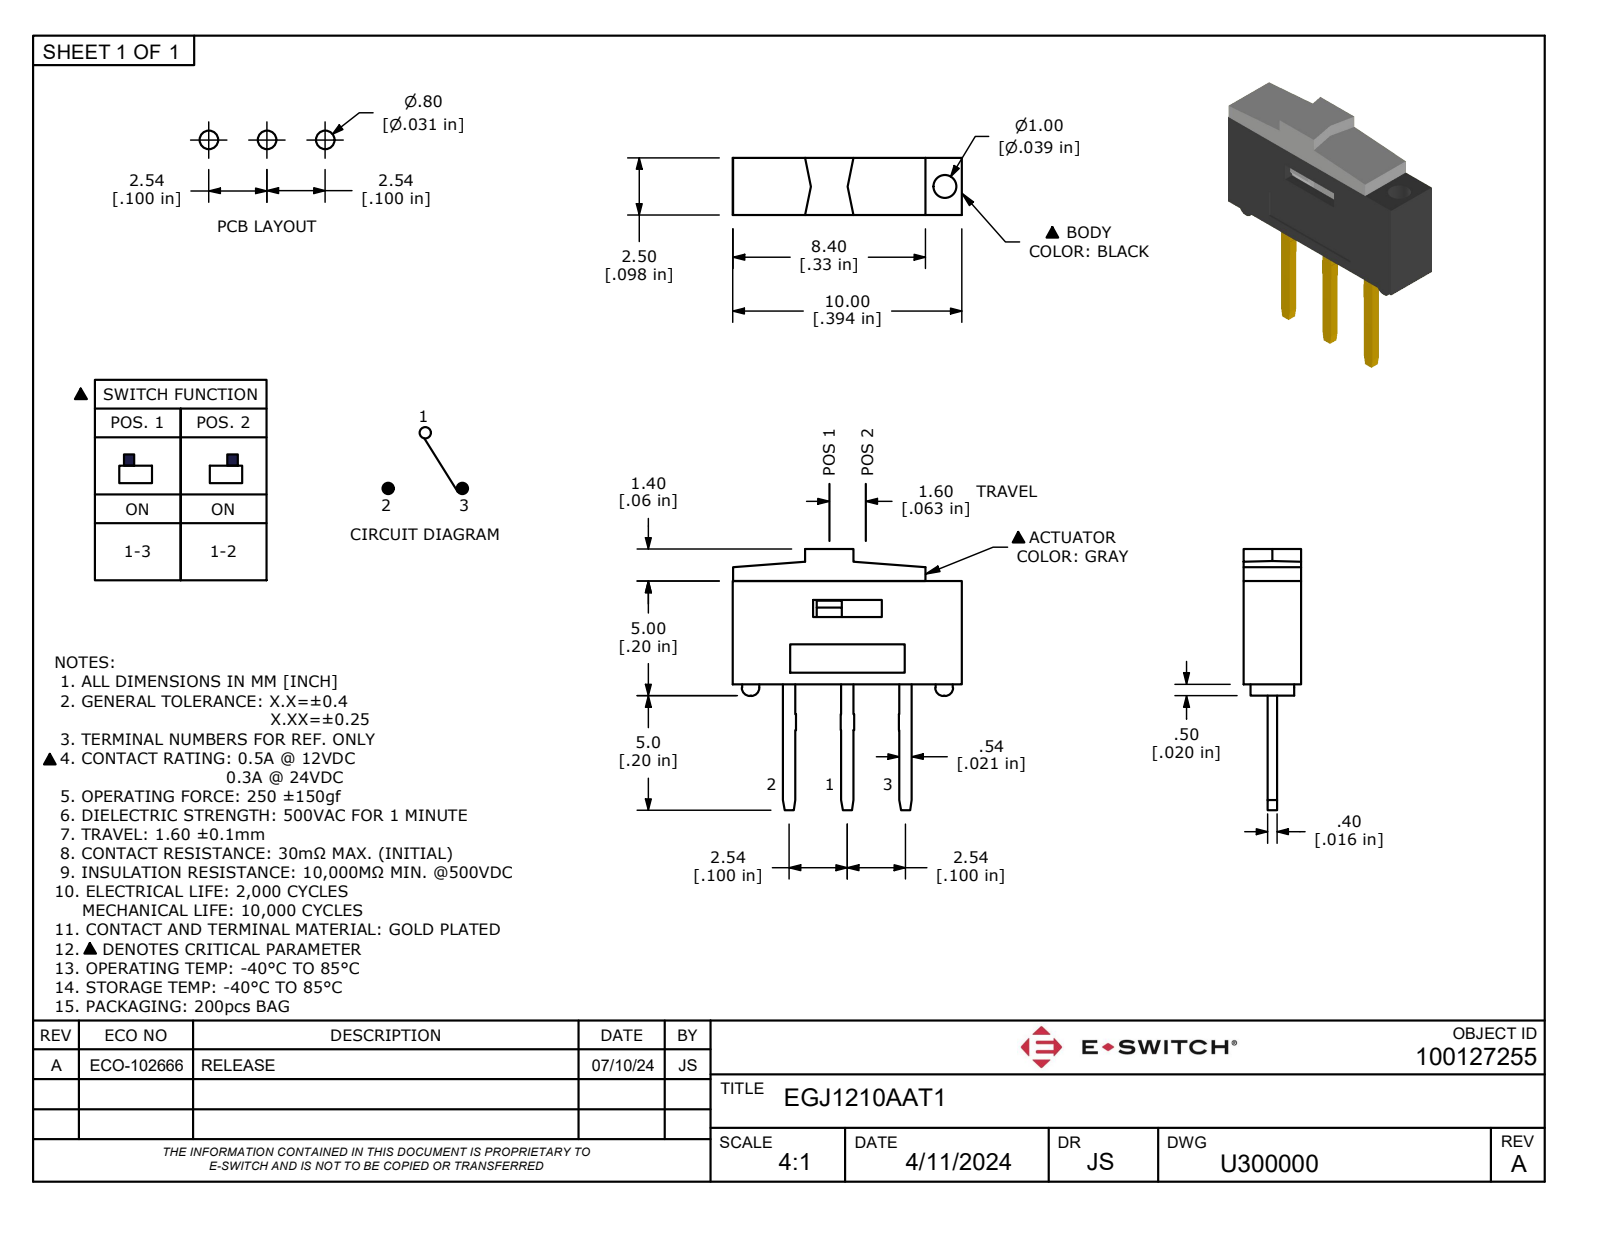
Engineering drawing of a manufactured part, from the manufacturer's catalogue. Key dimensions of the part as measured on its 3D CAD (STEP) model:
Part name (STEP PRODUCT): EGJ1210AAT1
STEP written by: Autodesk Inventor 2022 (AUTOMOTIVE_DESIGN)
Units: inches
Bodies: 1 solid, 105 faces (100 planar, 5 cylindrical, 0 other)
Overall size (bounding box): 0.449 × 0.394 × 0.098
Volume: 0.006 in³ · Surface area: 0.528 in²
Round holes (diameter × count): ⌀0.039 ×1
Partial cylindrical surfaces — rounded edges, fillets, slot ends (radius × count): R0.014 ×4
Main face-to-face distances: 0.017, 0.081, 0.098, 0.02, 0.065, 0.037, 0.062, 0.079, 0.041, 0.057
